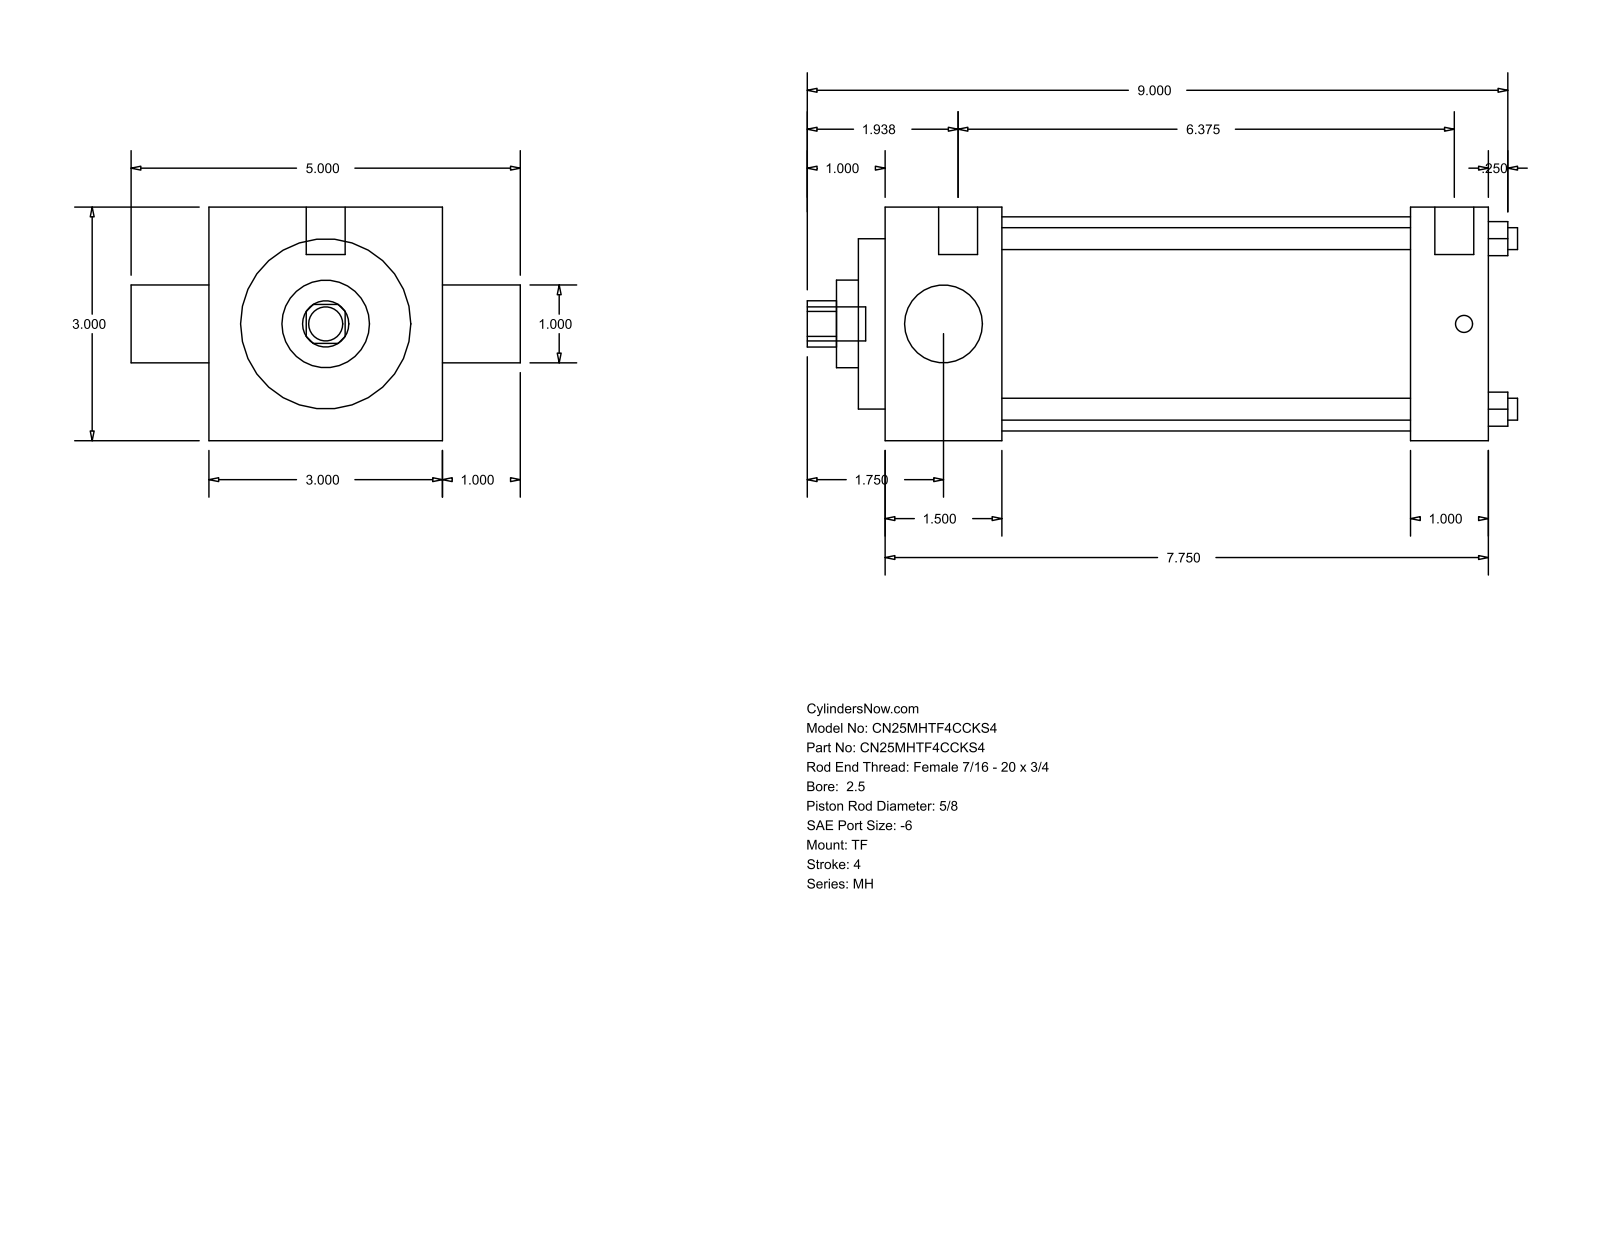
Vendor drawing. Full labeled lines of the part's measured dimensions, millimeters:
Part name (STEP PRODUCT): MH_TF__0250_0.625
STEP written by: GSSL Pune (CONFIG_CONTROL_DESIGN)
Units: millimetres
Bodies: 0 solids, 86 faces (61 planar, 25 cylindrical, 0 other)
Overall size (bounding box): 231.78 × 127 × 76.2
Round holes (diameter × count): ⌀7.14 ×4, ⌀15.88 ×1, ⌀25.4 ×1, ⌀28.57 ×1, ⌀55.55 ×1, ⌀69.85 ×1
Round bosses / shafts (diameter × count): ⌀5.56 ×3, ⌀12.7 ×2, ⌀11.11 ×1
Partial cylindrical surfaces — rounded edges, fillets, slot ends (radius × count): R7.54 ×1
Main face-to-face distances: 76.2, 196.85, 25.4, 38.1, 158.75, 171.45, 133.35, 8.73, 46.83, 180.18
Hole centre spacings: 39.33, 55.62, 78.66
